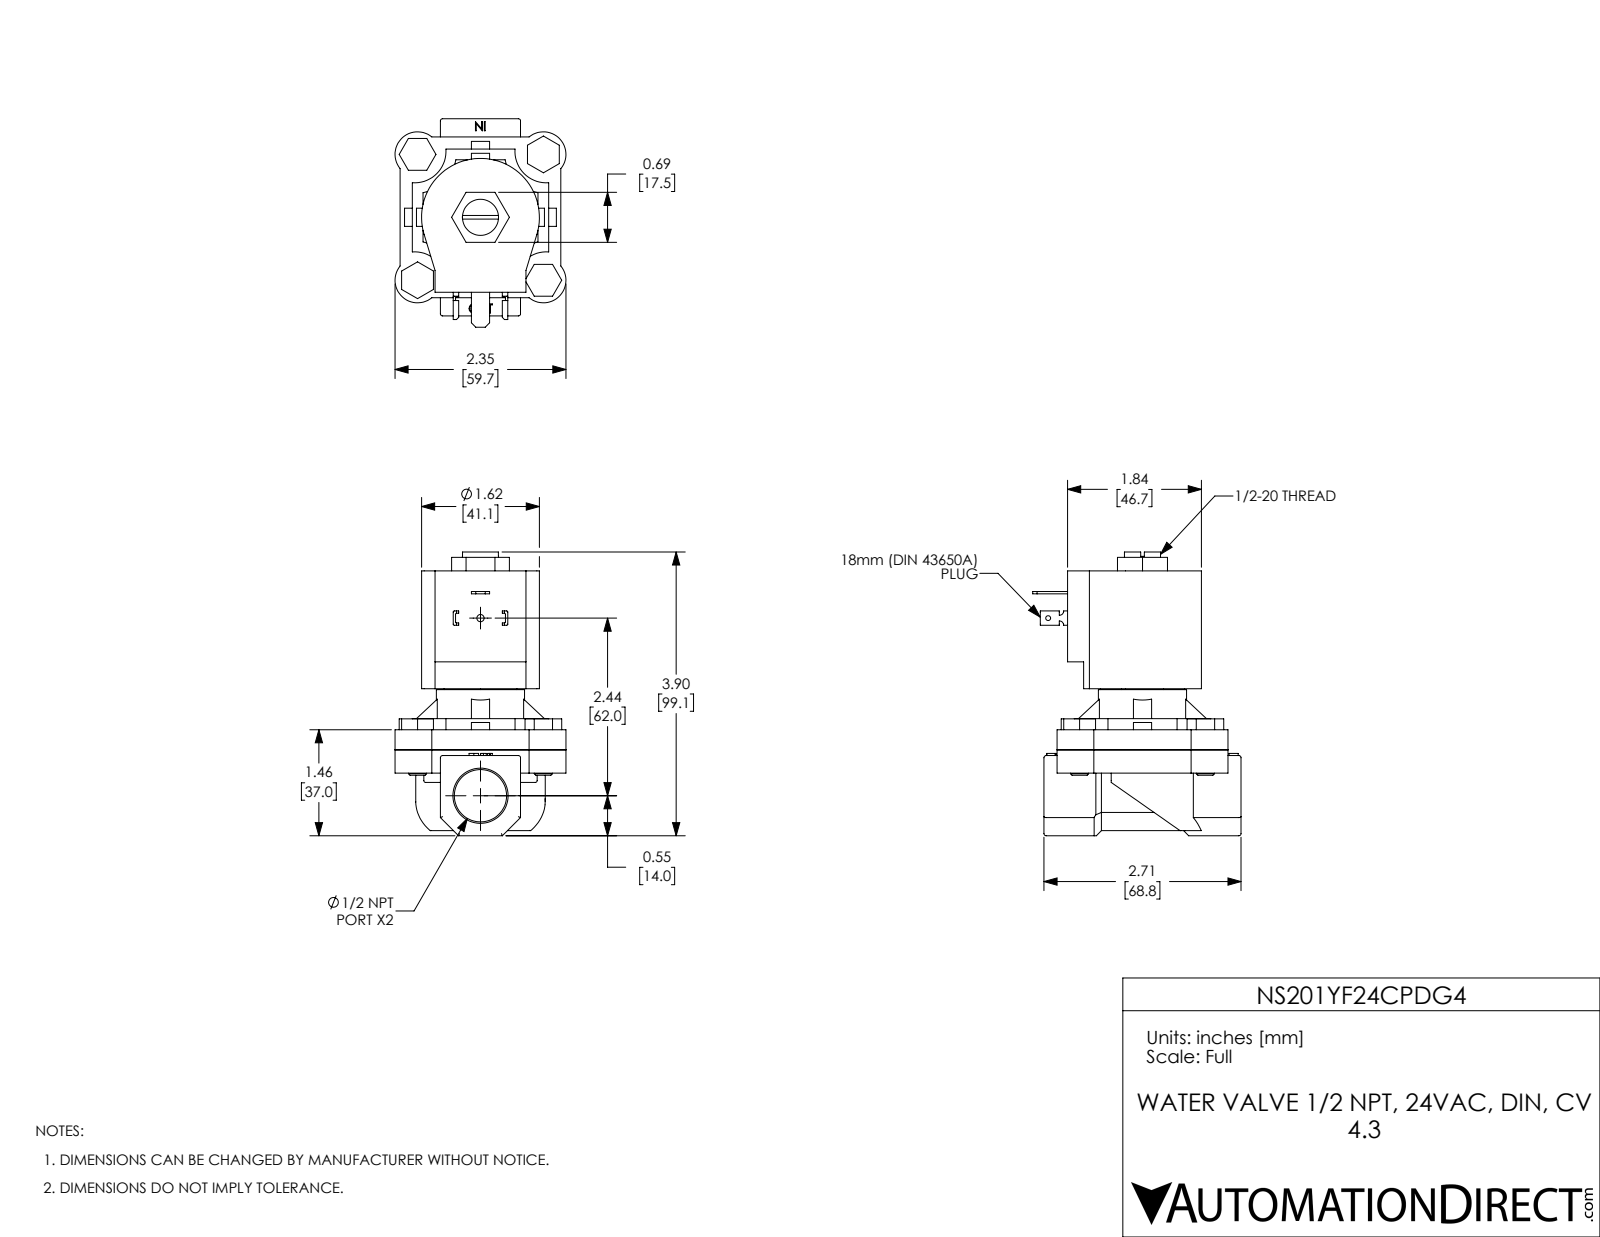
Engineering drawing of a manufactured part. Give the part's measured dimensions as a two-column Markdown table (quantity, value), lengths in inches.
| quantity | value |
| --- | --- |
| part name | NS201YF24CPDG4 |
| STEP written by | SolidWorks 2021 (CONFIG_CONTROL_DESIGN) |
| units | inches |
| bodies | 11 solids, 385 faces (239 planar, 113 cylindrical, 33 other) |
| overall size | 3.9 × 2.865 × 2.35 |
| volume | 10.07 in³ |
| surface area | 67.48 in² |
| round holes (diameter × count) | 0.25 × 4, 0.067 × 1, 0.1 × 1, 0.496 × 1, 0.512 × 1, 0.719 × 1, 1.155 × 1 |
| round bosses / shafts (diameter × count) | 0.248 × 4, 1.213 × 1 |
| partial cylindrical surfaces (radius × count) | 0.03 × 15, 0.015 × 8, 0.31 × 4, 0.432 × 4, 0.579 × 4, 0.06 × 2, 0.81 × 1, 0.89 × 1 |
| main face-to-face distances | 0.276, 2.459, 2.183, 0.32, 0.596, 2.779, 0.554, 1.656, 0.25, 1.102 |
| hole center spacings | 1.223, 1.73, 2.446, 2.441 |
